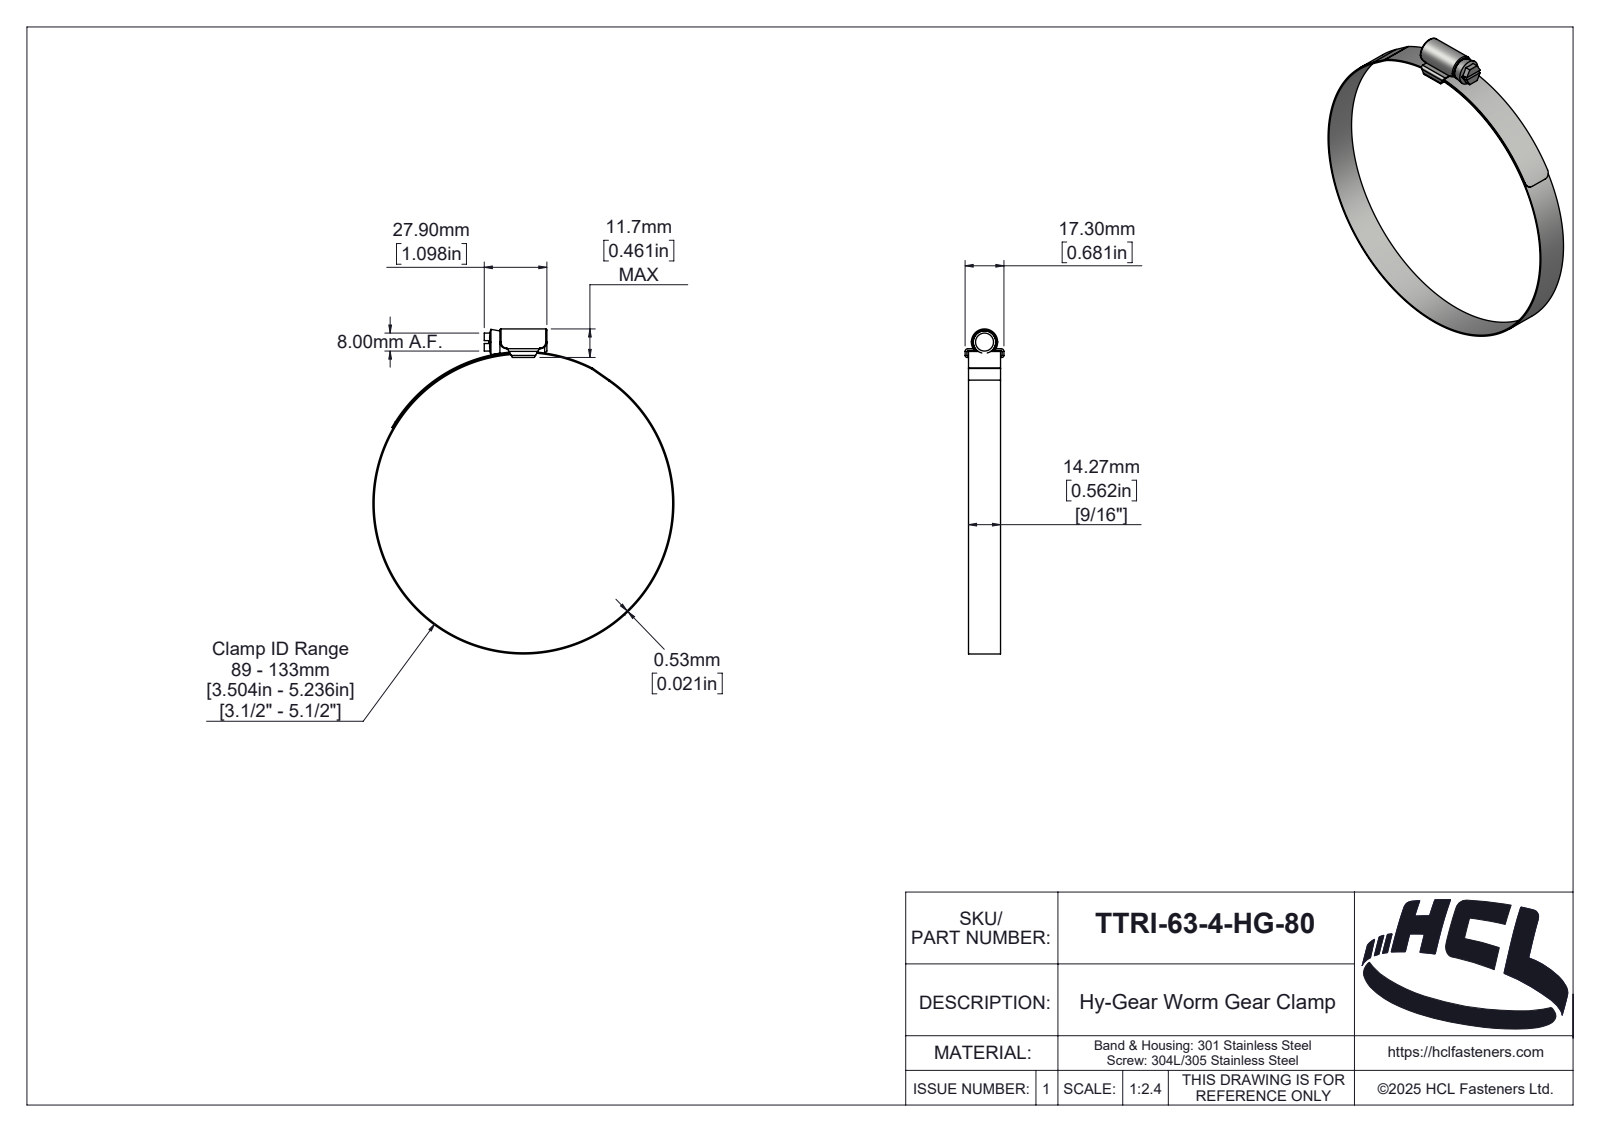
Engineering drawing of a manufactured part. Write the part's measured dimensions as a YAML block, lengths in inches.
part_name: "TRI-50-0-HG-80"
step_written_by: "SolidWorks 2025 (AUTOMOTIVE_DESIGN)"
units: inches
bodies: {solids: 3, faces: 189, planar: 39, cylindrical: 89, other: 61}
overall_size: [5.698, 5.278, 0.681]
volume: 0.397
surface_area: 26.84
round_holes:
  - {diameter: 5.236, count: 1}
round_bosses_or_shafts:
  - {diameter: 5.278, count: 1}
  - {diameter: 0.394, count: 1}
partial_cylinders:
  - {radius: 0.02, count: 6}
  - {radius: 0.118, count: 4}
  - {radius: 0.004, count: 2}
  - {radius: 0.035, count: 2}
  - {radius: 0.047, count: 2}
  - {radius: 0.018, count: 1}
  - {radius: 0.074, count: 1}
  - {radius: 0.079, count: 1}
face_to_face_distances: [0.031, 0.561, 0.122, 0.021, 0.091, 0.154, 1.098, 0.06, 0.621, 0.65]
